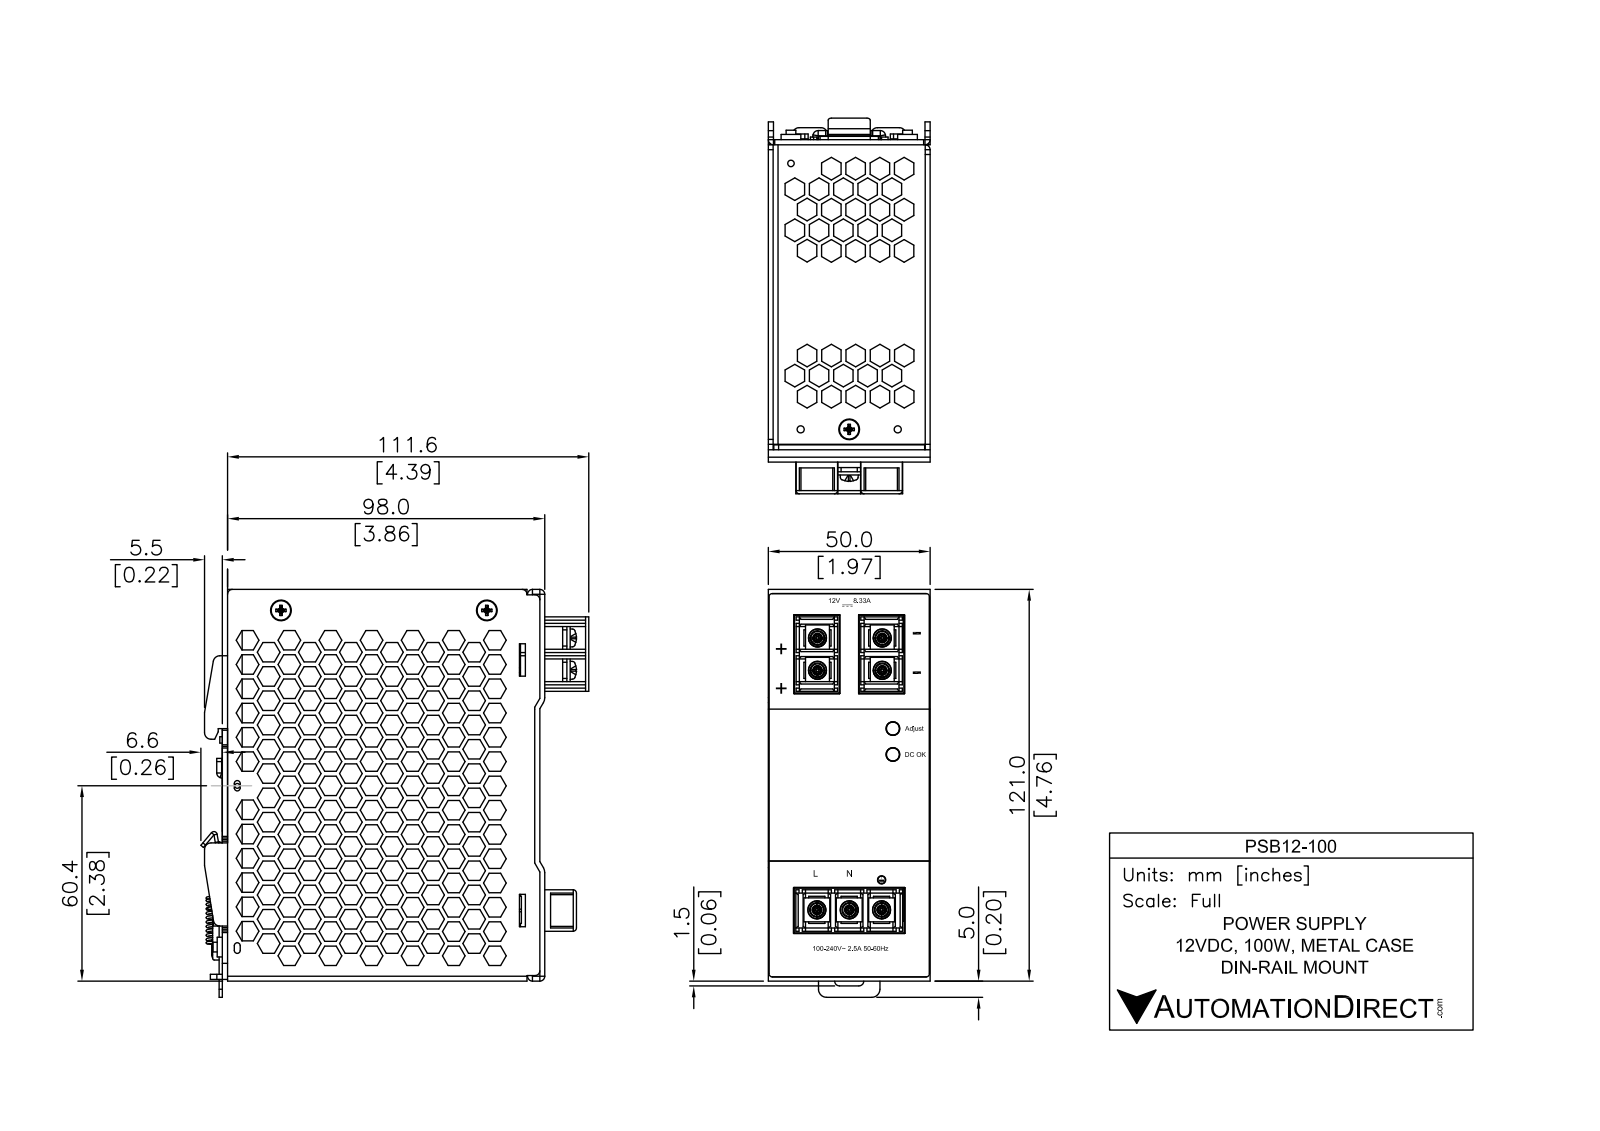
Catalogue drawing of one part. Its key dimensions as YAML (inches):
part_name: "PSB12-100"
step_written_by: "SolidWorks 2011 (CONFIG_CONTROL_DESIGN)"
units: inches
bodies: {solids: 1, faces: 3540, planar: 3357, cylindrical: 103, other: 80}
overall_size: [4.946, 4.612, 1.97]
volume: 25.61
surface_area: 183.7
round_holes:
  - {diameter: 0.145, count: 2}
round_bosses_or_shafts:
  - {diameter: 0.23, count: 4}
  - {diameter: 0.125, count: 4}
  - {diameter: 0.205, count: 3}
partial_cylinders:
  - {radius: 0.06, count: 24}
  - {radius: 0.03, count: 13}
  - {radius: 0.05, count: 6}
  - {radius: 0.04, count: 3}
  - {radius: 0.04, count: 2}
  - {radius: 0.075, count: 2}
  - {radius: 0.13, count: 2}
  - {radius: 0.01, count: 1}
face_to_face_distances: [0.353, 1.613, 0.28, 0.073, 1.893, 1.54, 1.26, 0.06, 0.075, 1.966]
hole_center_spacings: [0.3]
